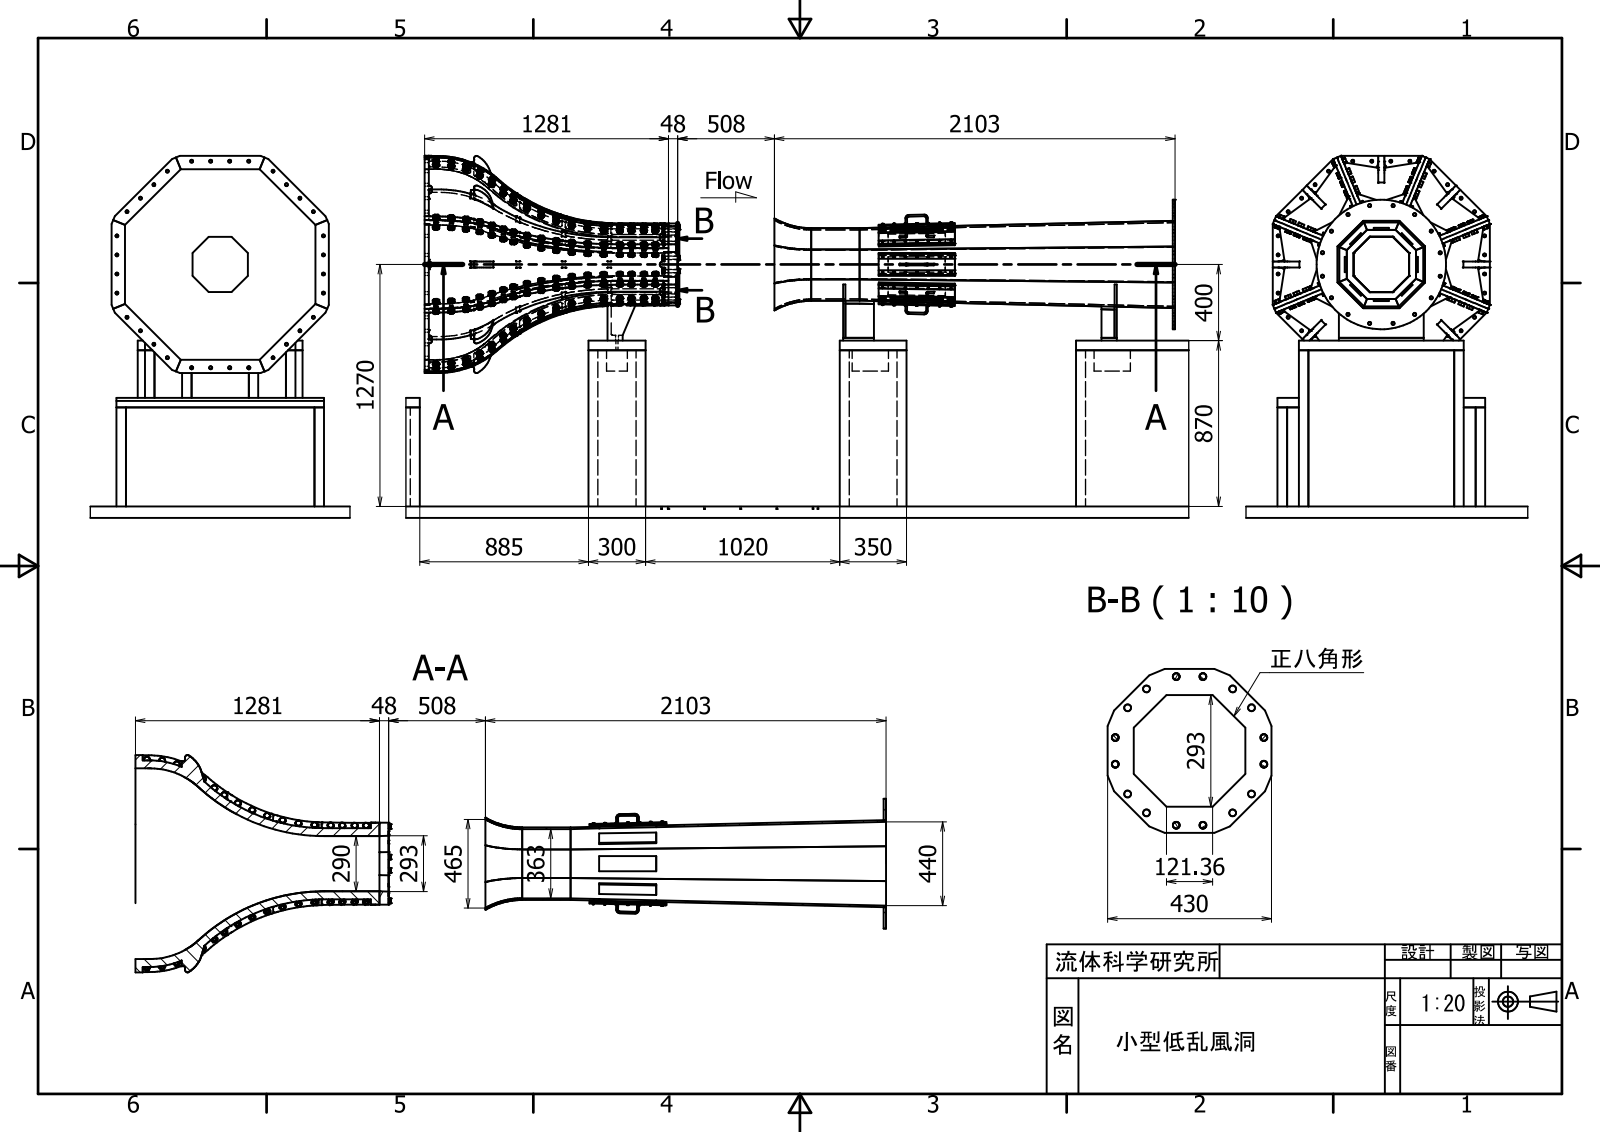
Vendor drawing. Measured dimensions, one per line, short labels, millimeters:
name: All_Assembly2_20230612; 小型低乱調風洞 (開放_コレクタ1 ); 測定部台座; 測定部台座A (+8 more)
written by: Autodesk Inventor 2023 (AUTOMOTIVE_DESIGN)
unit: mm
bodies: 528 solids, 12484 faces (6113 planar, 1524 cylindrical, 4847 other)
size: 6995 × 4490 × 1900
volume: 2 581 000 000 mm³; area: 110 800 000 mm²
holes: 150× ⌀19, 136× ⌀17.5, 136× ⌀20, 112× ⌀5, 48× ⌀16, 44× ⌀15, 42× ⌀6.65, 16× ⌀18, 4× ⌀7.13, 4× ⌀14, 4× ⌀14.5, 2× ⌀10.8
bosses: 136× ⌀30, 136× ⌀20, 112× ⌀7, 112× ⌀4, 16× ⌀24, 8× ⌀16, 1× ⌀680
rounds: 153× R7, 16× R13, 12× R16, 8× R150
face distances: 60, 50, 300, 350, 112.5, 927.5, 815, 9, 880, 820
hole spacings: 100, 80, 144.22, 120, 60, 85, 424.85, 180
